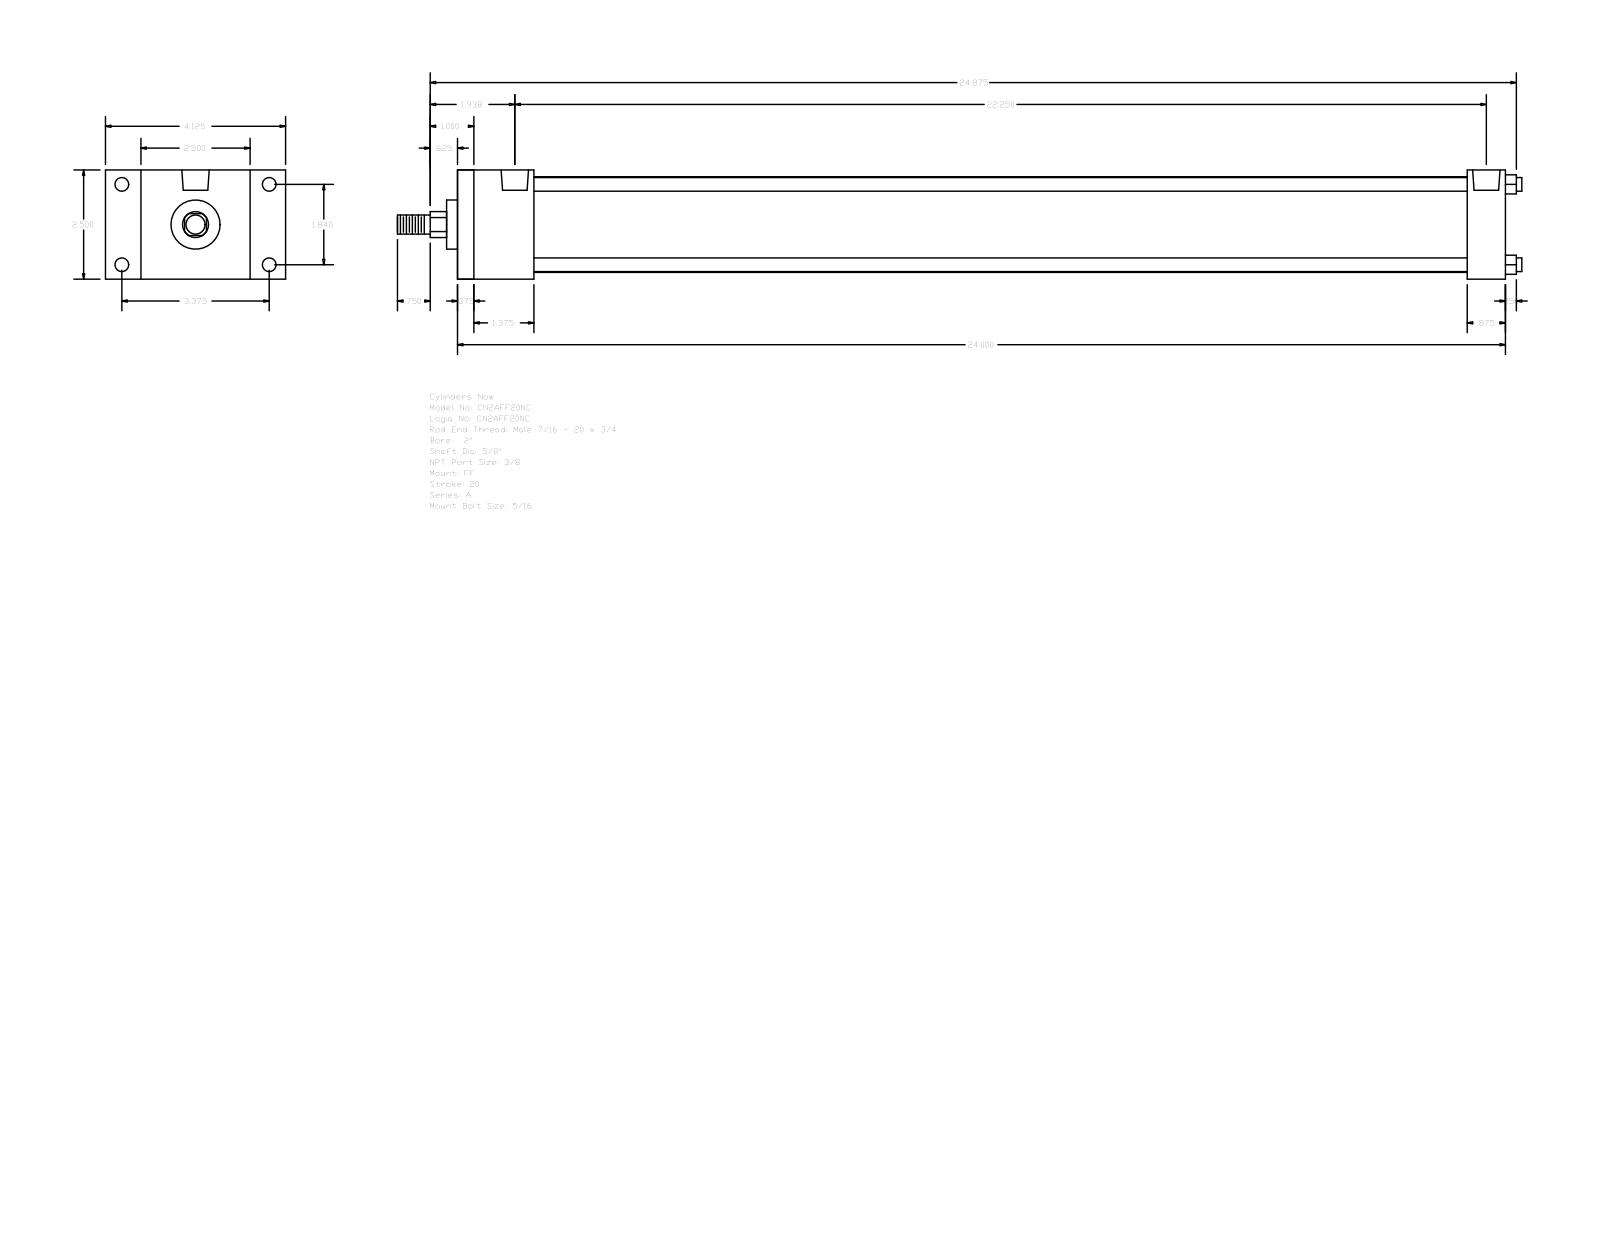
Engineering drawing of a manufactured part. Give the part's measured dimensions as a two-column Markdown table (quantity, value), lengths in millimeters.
| quantity | value |
| --- | --- |
| part name | A_FF__0200_0.625 |
| STEP written by | GSSL Pune (CONFIG_CONTROL_DESIGN) |
| units | millimeters |
| bodies | 0 solids, 92 faces (64 planar, 28 cylindrical, 0 other) |
| overall size | 654.05 × 104.78 × 63.5 |
| round holes (diameter × count) | 5.56 × 4, 7.94 × 4, 15.93 × 2 |
| round bosses / shafts (diameter × count) | 7.94 × 4, 55.63 × 1, 28.57 × 1, 15.88 × 1, 11.11 × 1 |
| partial cylindrical surfaces (radius × count) | 7.54 × 1 |
| main face-to-face distances | 63.5, 609.6, 9.52, 600.08, 34.93, 44.45, 587.37, 577.85, 542.92, 565.15 |
| hole center spacings | 46.74, 85.72, 97.63, 557.2, 3.97, 3.98, 561.17, 561.18 |
